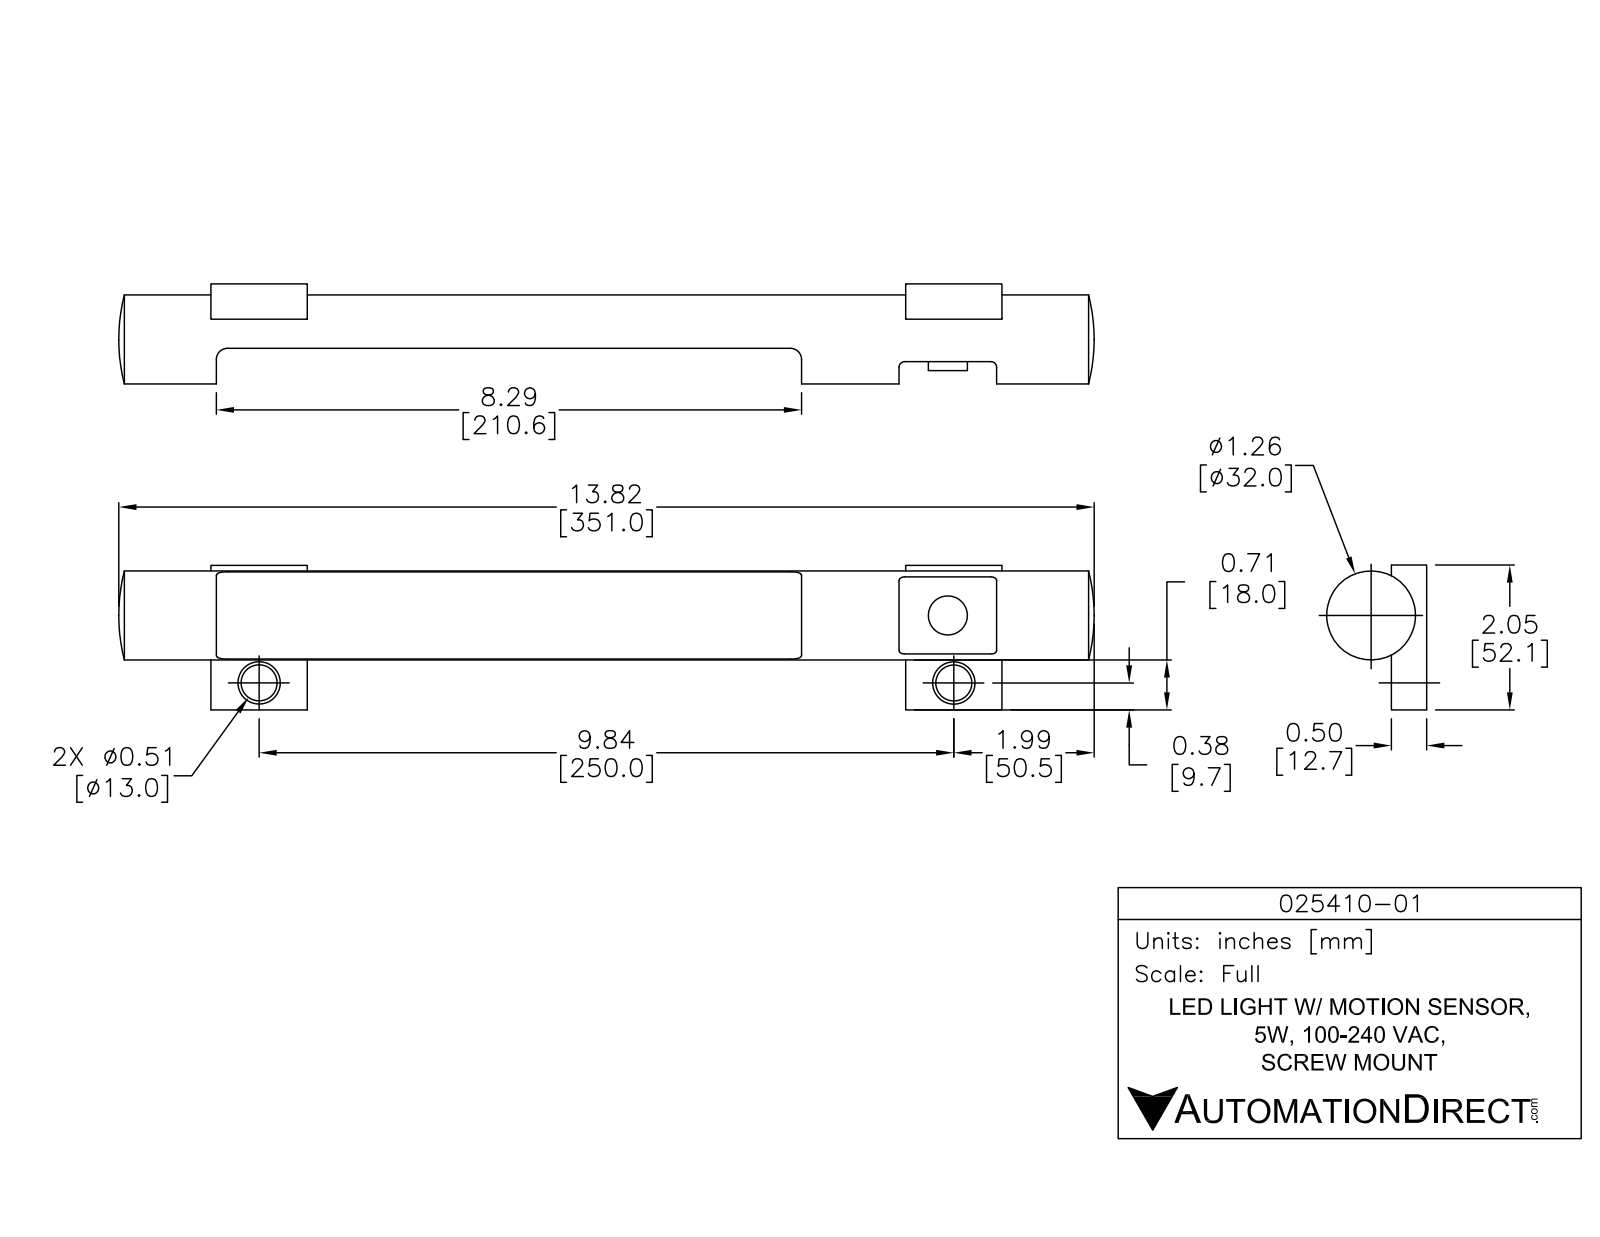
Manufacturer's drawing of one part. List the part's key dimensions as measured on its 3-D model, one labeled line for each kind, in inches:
Part name (STEP PRODUCT): 025410-01
STEP written by: SolidWorks 2013 (AUTOMOTIVE_DESIGN)
Units: inches
Bodies: 1 solid, 163 faces (90 planar, 35 cylindrical, 38 other)
Overall size (bounding box): 13.758 × 2.045 × 1.535
Volume: 14.77 in³ · Surface area: 66.91 in²
Round holes (diameter × count): ⌀0.077 ×2, ⌀0.235 ×2, ⌀0.892 ×1
Round bosses / shafts (diameter × count): ⌀0.073 ×2, ⌀1.26 ×1
Partial cylindrical surfaces — rounded edges, fillets, slot ends (radius × count): R0.06 ×4, R0.095 ×4, R0.12 ×2, R0.2 ×2, R0.4 ×2, R0.629 ×2
Main face-to-face distances: 0.905, 2.045, 0.03, 0.325, 0.45, 0.1, 0.03, 0.545, 0.55, 0.355
Hole centre spacings: 0.101, 0.2, 9.671, 9.772
